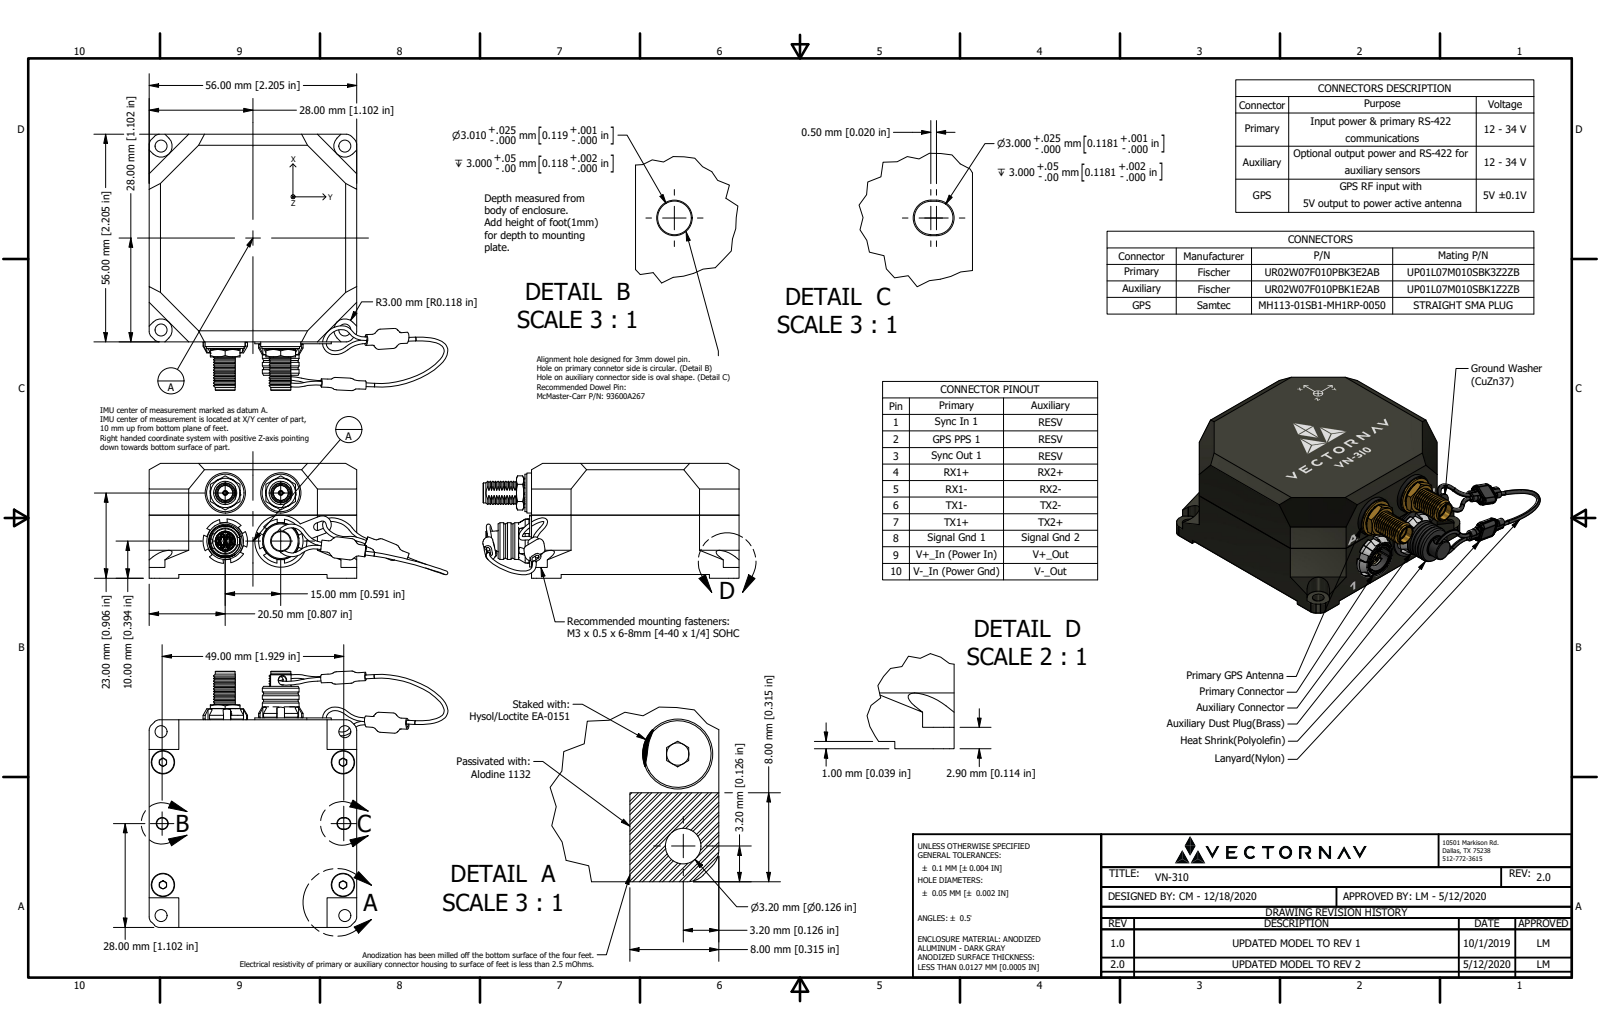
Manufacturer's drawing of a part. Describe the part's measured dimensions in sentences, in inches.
The part is named "VN-310_Assembly_Rev2_HW3; CaseBottom Assembly_Rev2; Case_Bottom_Rev2; Fisher_UR02W07_F010P_BK1 (+5 more)". Its 3-D file was written by "Autodesk Inventor 2021 (AUTOMOTIVE_DESIGN)". It is 25 solids with 3293 faces: 1183 planar, 1046 cylindrical and 1064 other. Overall it measures 3.173 by 2.722 by 1.22 inches. Its volume is 2.221 cubic inches and its surface area 57.82 square inches. Round holes: 20 of diameter 0.023, 20 of diameter 0.039, 20 of diameter 0.041, 8 of diameter 0.126, 6 of diameter 0.079, 4 of diameter 0.097, 4 of diameter 0.248, 2 of diameter 0.035, 2 of diameter 0.038, 2 of diameter 0.05, 2 of diameter 0.161, 2 of diameter 0.182. Round bosses or shafts: 22 of diameter 0.031, 20 of diameter 0.039, 20 of diameter 0.024, 20 of diameter 0.016, 6 of diameter 0.177, 4 of diameter 0.236, 4 of diameter 0.118, 4 of diameter 0.039. Partial cylindrical surfaces (rounded edges, fillets, slot ends): 75 of radius 0.039, 58 of radius 0.197, 24 of radius 0.089, 16 of radius 0.02, 16 of radius 0.135, 16 of radius 0.135, 16 of radius 0.18, 16 of radius 0.18. The main face-to-face distances are 0.079, 1.102, 1.181, 0.138, 0.551, 2.205, 2.067, 0.02, 0.63, 0.472. The hole center spacings are 0.066, 0.591, 0.047, 0.123, 0.046, 0.061, 0.077, 0.087.
